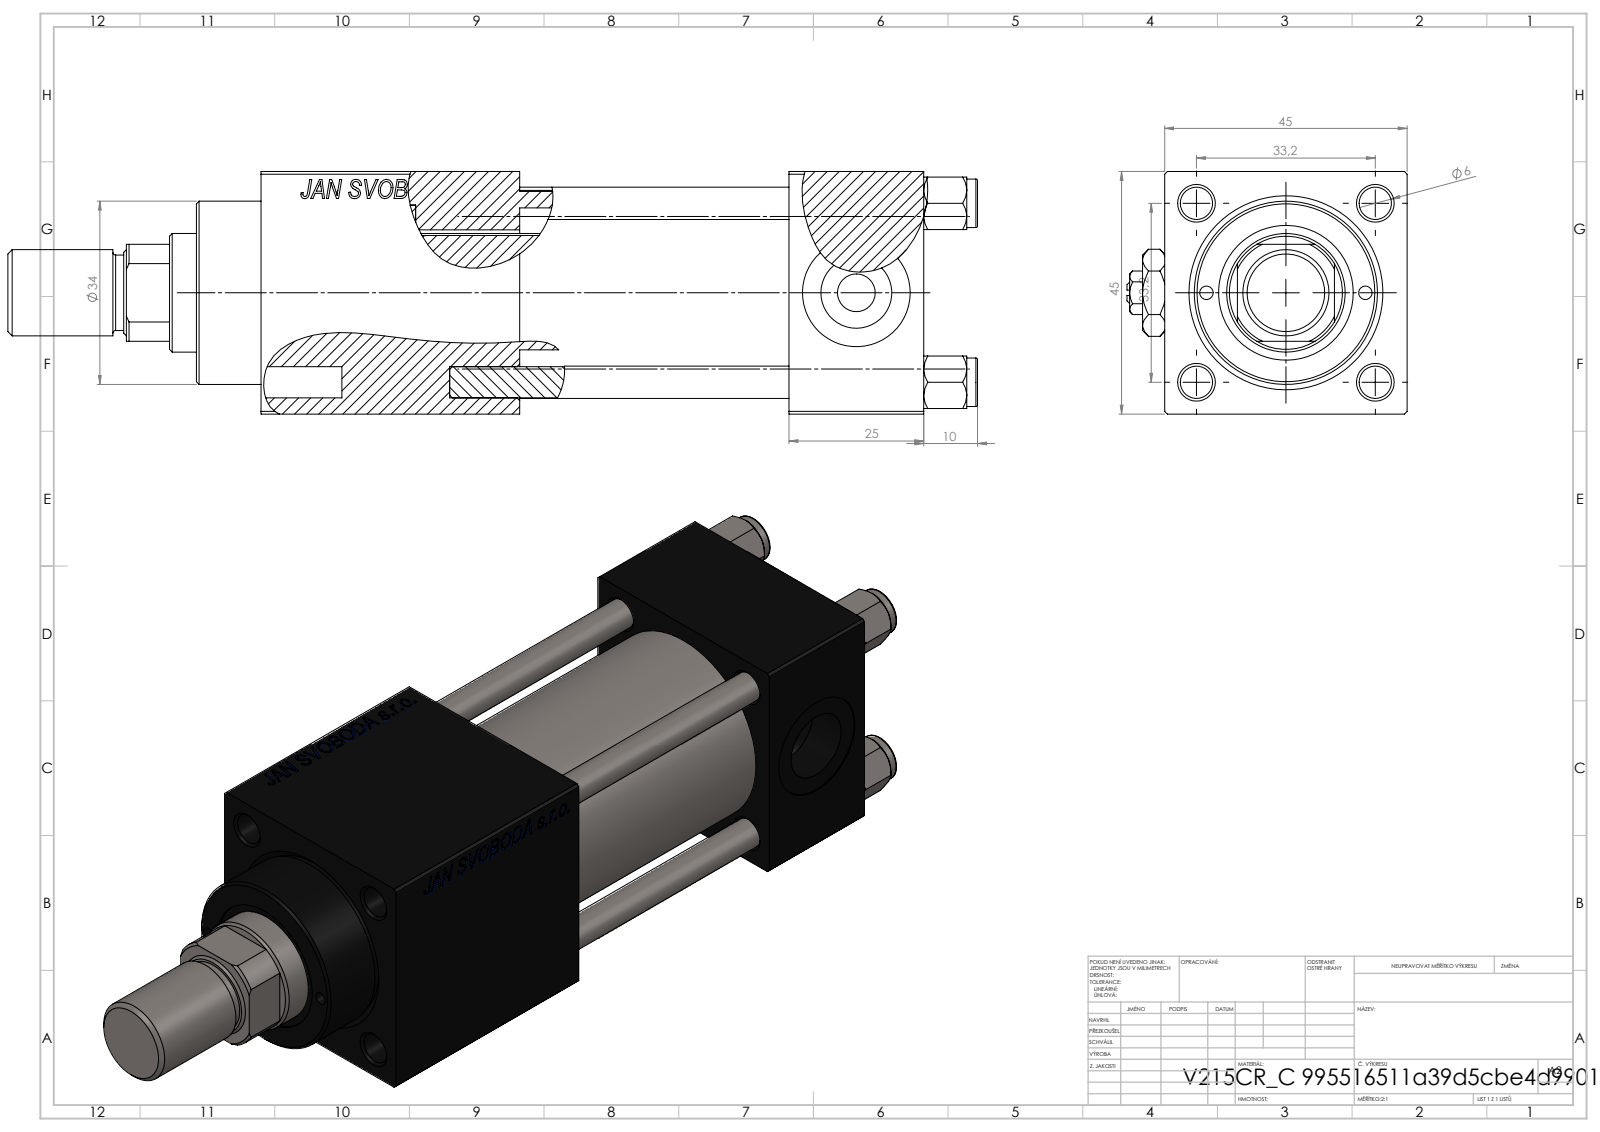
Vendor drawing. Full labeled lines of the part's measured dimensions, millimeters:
Part name (STEP PRODUCT): ROD_END_AH; NUT_M5_C; V215CR_C_Body; V215CR_VCP_C (+3 more)
STEP written by: SolidWorks 2019 (CONFIG_CONTROL_DESIGN)
Units: millimetres
Bodies: 13 solids, 1220 faces (554 planar, 102 cylindrical, 564 other)
Overall size (bounding box): 180 × 52 × 45
Volume: 213 153 mm³ · Surface area: 74 189 mm²
Round holes (diameter × count): ⌀6 ×4, ⌀2.5 ×2, ⌀7 ×2, ⌀13.16 ×2, ⌀20 ×2, ⌀10.5 ×1, ⌀22 ×1, ⌀24 ×1, ⌀25 ×1, ⌀32 ×1, ⌀33 ×1
Round bosses / shafts (diameter × count): ⌀9 ×4, ⌀38 ×1, ⌀34 ×1, ⌀16 ×1, ⌀14 ×1
Partial cylindrical surfaces — rounded edges, fillets, slot ends (radius × count): R10.5 ×1
Main face-to-face distances: 45, 25, 123, 50, 75, 98, 48, 94.3, 69.3, 19.3
Hole centre spacings: 16.7, 23.48, 33.2, 35.47, 14.75, 46.95, 29.5, 75.5
